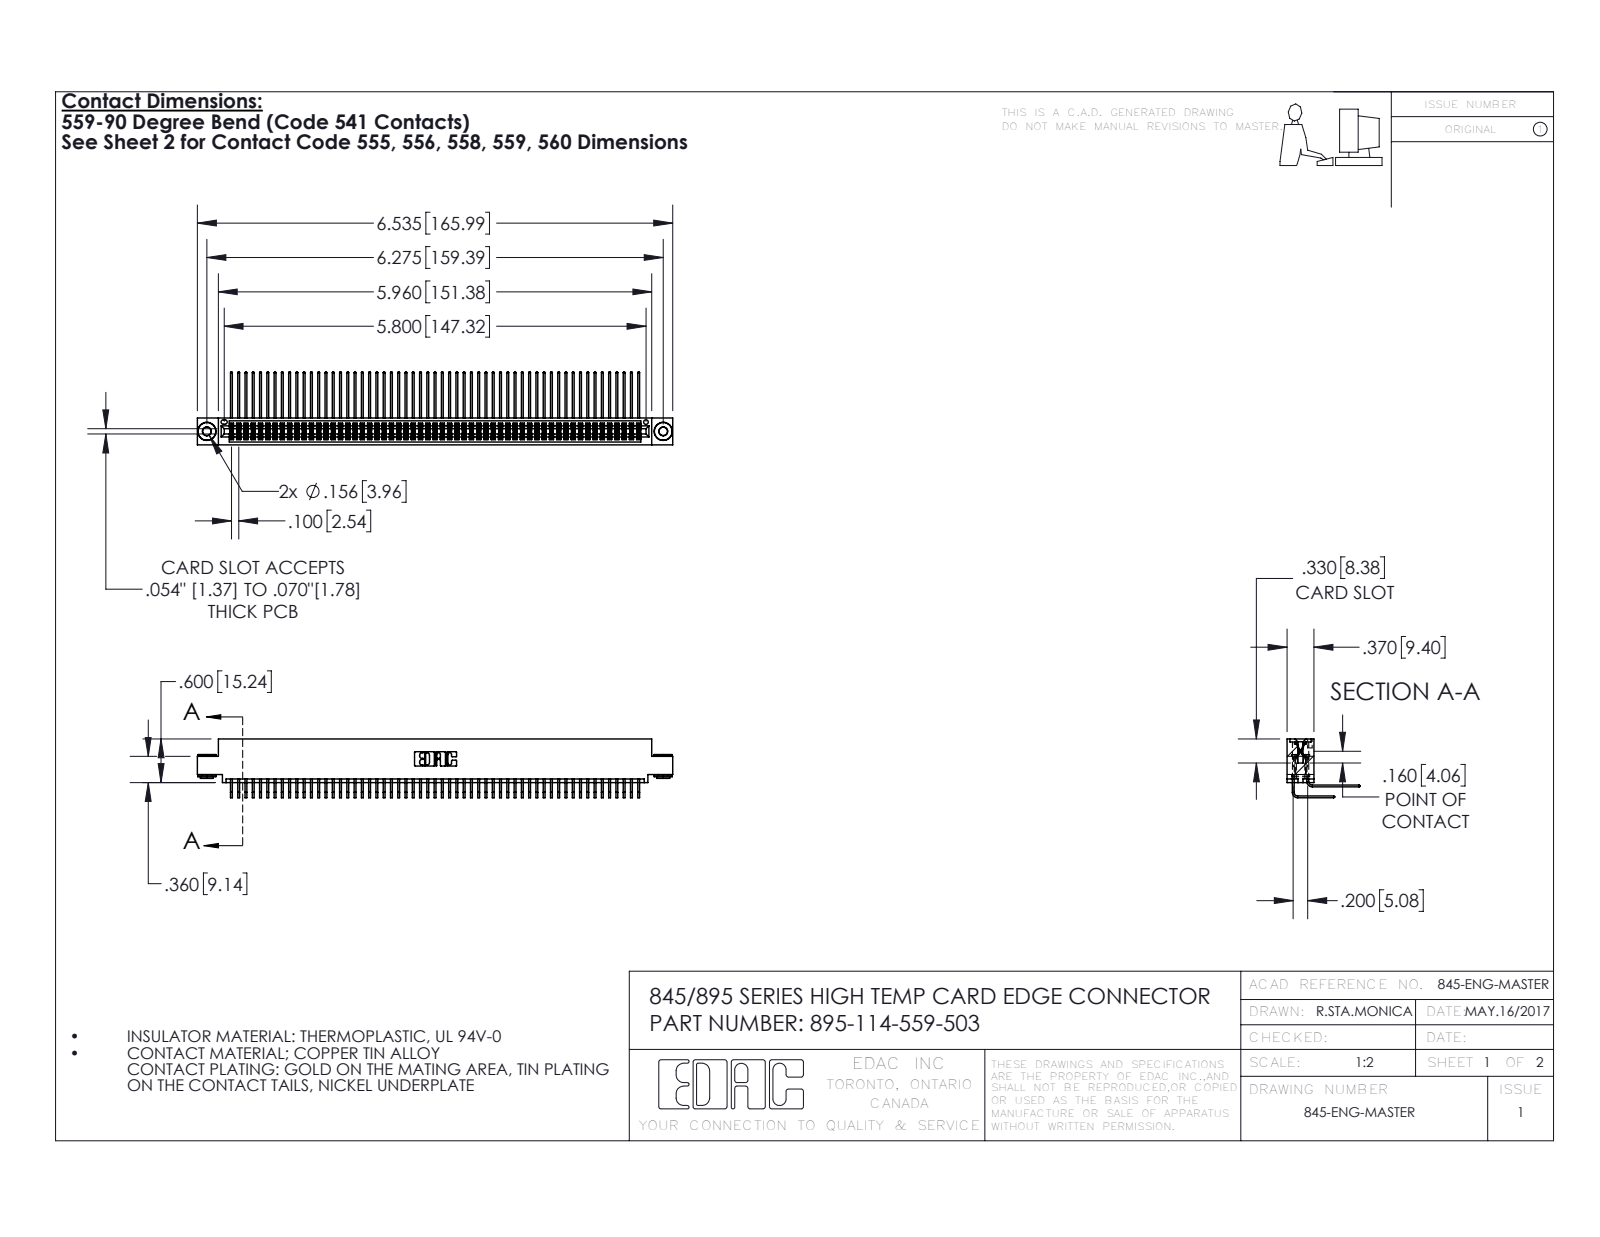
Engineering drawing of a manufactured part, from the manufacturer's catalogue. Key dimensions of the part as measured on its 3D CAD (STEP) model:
Part name (STEP PRODUCT): 345-292-001_558 559 Tail - 1; 345 Part_0.110 Offset - 0.156 Dia-TH; 345-250-002_345-250-002-102; 345-292-001_559 Tail - 2 (+1 more)
STEP written by: SolidWorks 2016 (CONFIG_CONTROL_DESIGN)
Units: inches
Bodies: 117 solids, 6096 faces (4084 planar, 2004 cylindrical, 8 other)
Overall size (bounding box): 6.535 × 1.005 × 0.809
Volume: 1.029 in³ · Surface area: 44.35 in²
Round holes (diameter × count): ⌀0.116 ×2, ⌀0.156 ×2, ⌀0.064 ×1
Round bosses / shafts (diameter × count): ⌀0.25 ×2, ⌀0.18 ×2, ⌀0.136 ×2
Partial cylindrical surfaces — rounded edges, fillets, slot ends (radius × count): R0.006 ×172, R0.01 ×22, R0.007 ×6, R0.031 ×6, R0.026 ×3, R0.014 ×2, R0.019 ×2, R0.022 ×2
Main face-to-face distances: 0.072, 0.298, 0.2, 0.37, 0.025, 0.098, 0.272, 0.225, 0.175, 0.15
Hole centre spacings: 0.27, 6.039, 6.275
